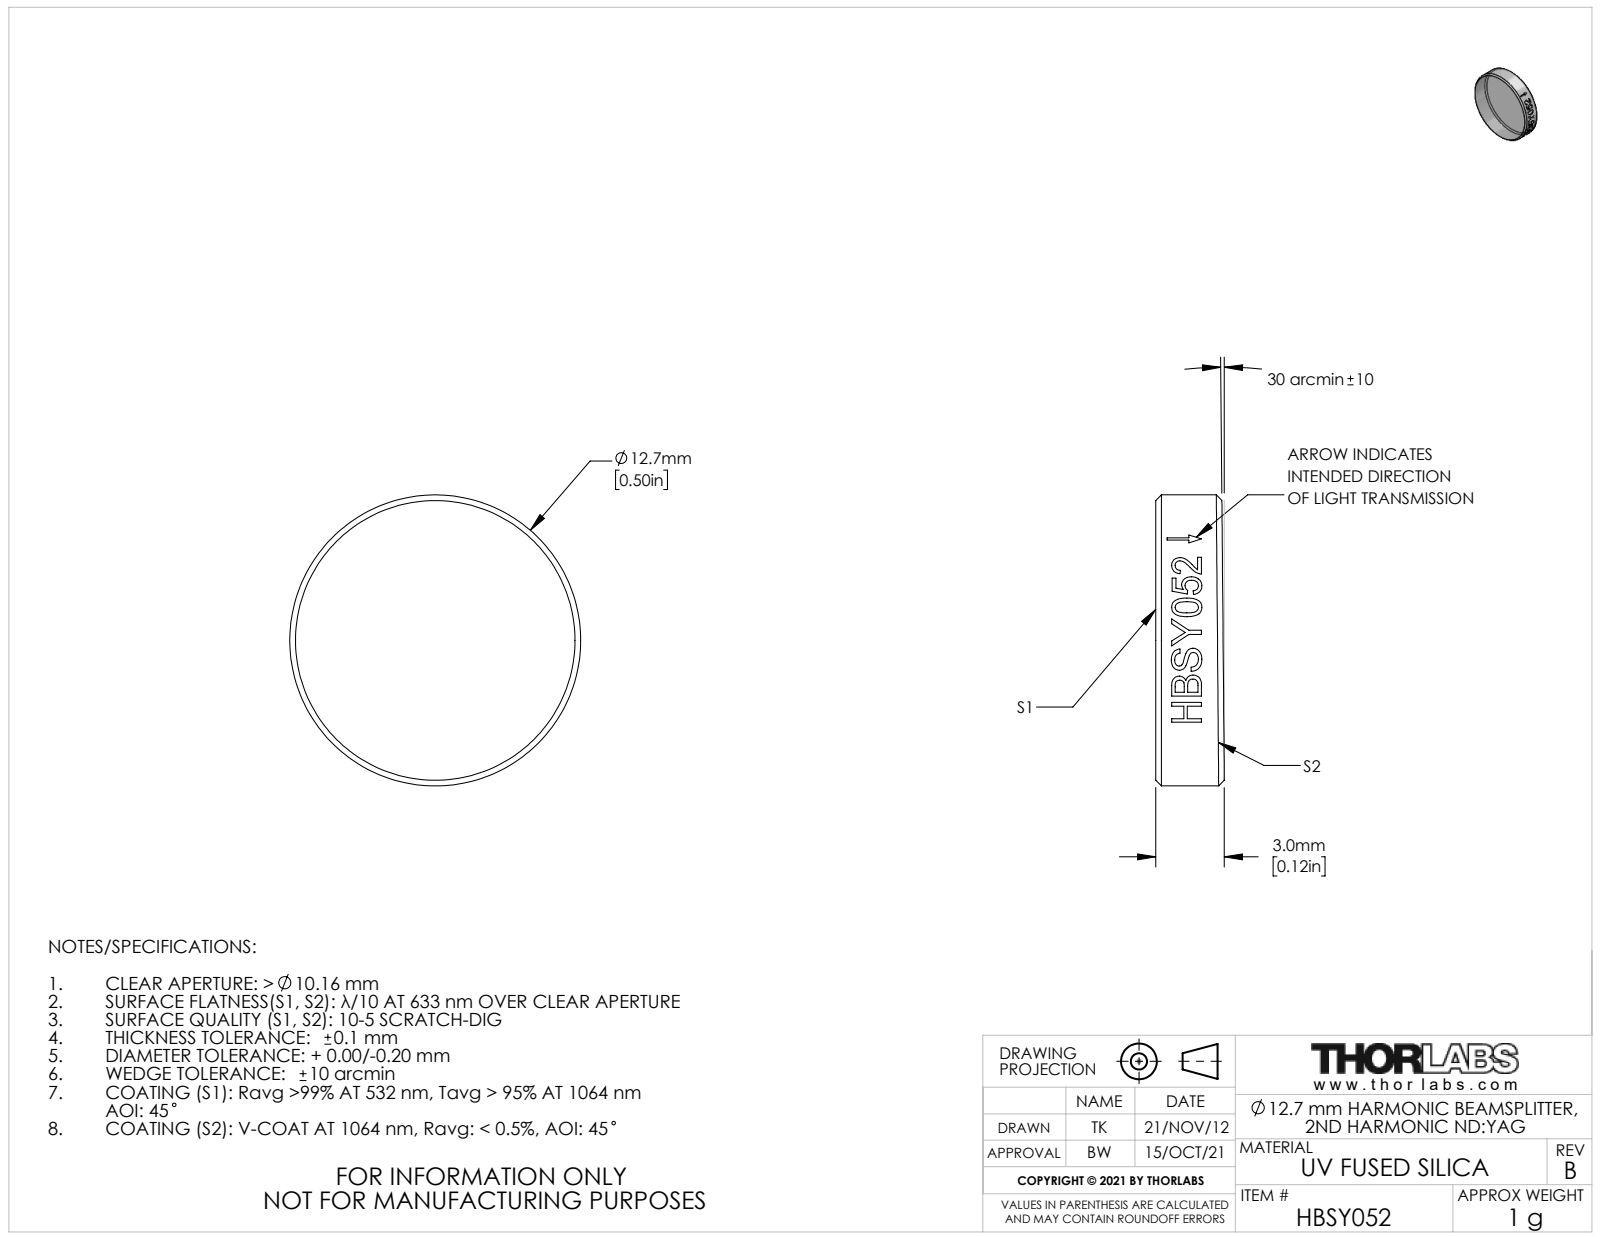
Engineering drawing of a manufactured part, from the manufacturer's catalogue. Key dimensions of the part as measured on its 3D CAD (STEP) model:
Part name (STEP PRODUCT): TTN006419-E0W
STEP written by: SolidWorks 2012 (CONFIG_CONTROL_DESIGN)
Units: millimetres
Bodies: 1 solid, 19 faces (2 planar, 13 cylindrical, 4 other)
Overall size (bounding box): 12.7 × 12.7 × 3
Volume: 370 mm³ · Surface area: 359 mm²
Round bosses / shafts (diameter × count): ⌀12.7 ×1
